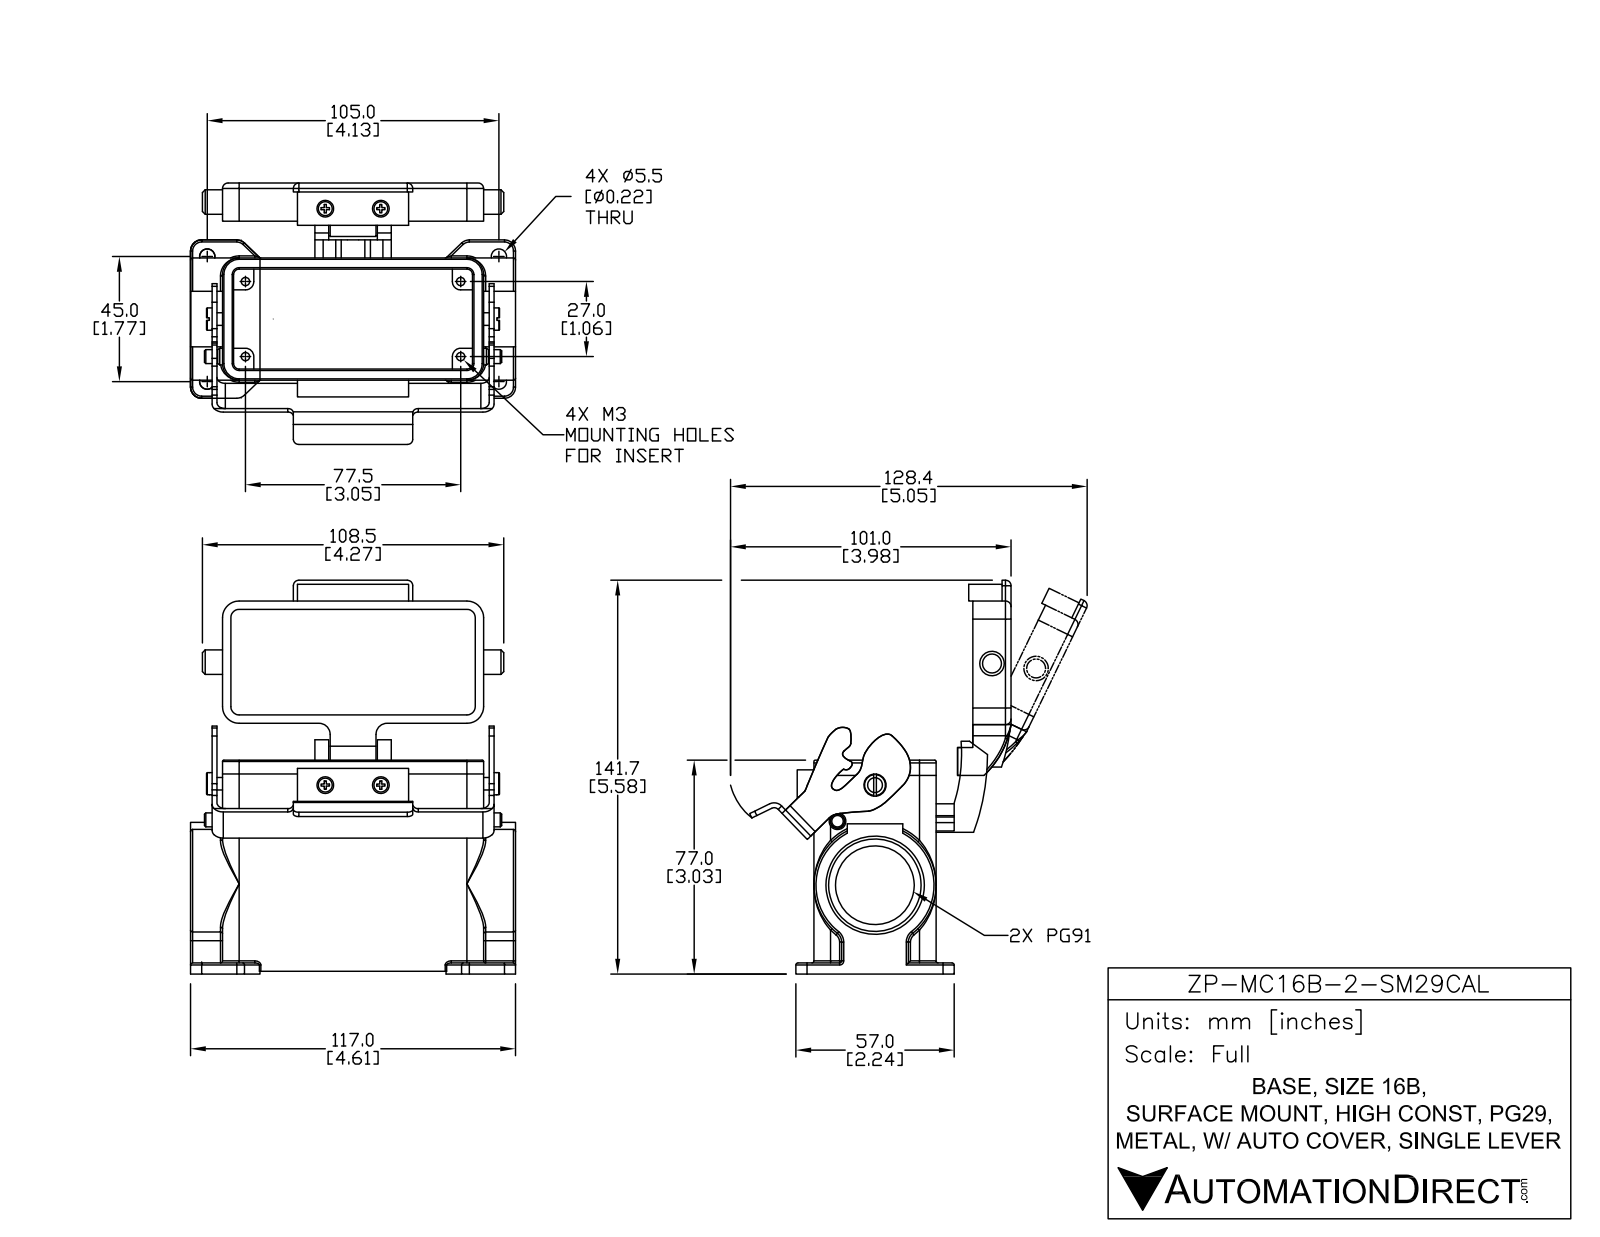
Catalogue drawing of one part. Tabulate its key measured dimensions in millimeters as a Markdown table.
| quantity | value |
| --- | --- |
| part name | ZP-MC16B-2-SM29CAL |
| STEP written by | SolidWorks 2014 (AUTOMOTIVE_DESIGN) |
| units | millimeters |
| bodies | 11 solids, 584 faces (242 planar, 194 cylindrical, 148 other) |
| overall size | 141.25 × 117 × 94.11 |
| volume | 156 428 mm³ |
| surface area | 86 953 mm² |
| round holes (diameter × count) | 3 × 4, 5.5 × 4, 4.5 × 1, 5.32 × 1, 30.5 × 1, 35.4 × 1 |
| round bosses / shafts (diameter × count) | 5 × 5, 8 × 2, 8.8 × 1, 6 × 1 |
| partial cylindrical surfaces (radius × count) | 0.75 × 25, 2 × 23, 4 × 14, 3 × 12, 0.5 × 8, 6 × 8, 21.95 × 2, 3.75 × 1 |
| main face-to-face distances | 4, 40, 44, 1.75, 36, 5, 1, 26.98, 30.98, 66.98 |
| hole center spacings | 15.95, 38.92, 91.89, 98.51, 28, 45, 78, 82.87 |
